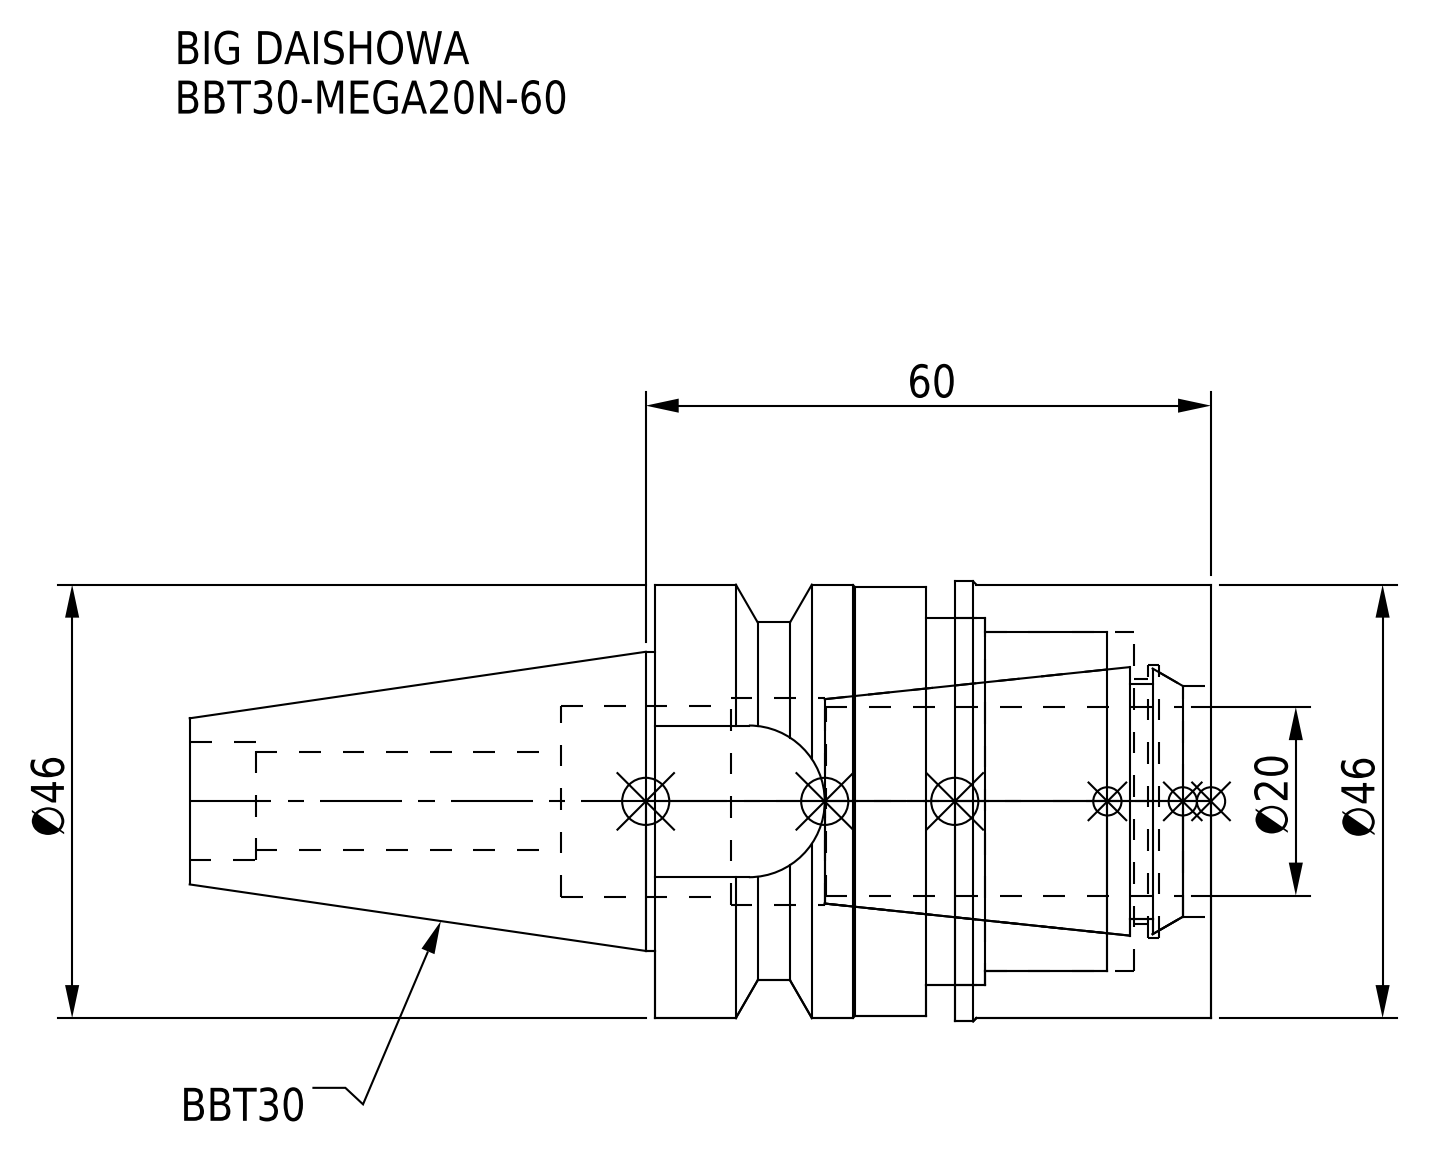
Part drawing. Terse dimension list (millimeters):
name: MGN20_1.stp; DXF_TEMP_ASSY_ASM_4_ASM.stp; BBT30MN20060-200_ASM.stp; BBT30-MEGA20N-60-200.stp (+3 more)
written by: SolidWorks 2019 (CONFIG_CONTROL_DESIGN)
unit: mm
bodies: 2 solids, 76 faces (22 planar, 40 cylindrical, 14 other)
size: 108.4 × 46.7 × 46.7
volume: 80 372 mm³; area: 28 097 mm²
holes: 1× ⌀10.4, 1× ⌀12.5, 1× ⌀20.3, 1× ⌀22, 1× ⌀24.5, 1× ⌀26, 1× ⌀29, 1× ⌀36, 1× ⌀39
bosses: 1× ⌀46.7, 1× ⌀46, 1× ⌀45.5, 1× ⌀31.75
rounds: 1× R8.05, 1× R19
face distances: 59, 27.2, 31.8, 8.2, 19, 50.8, 3, 30.2, 22, 28.8
